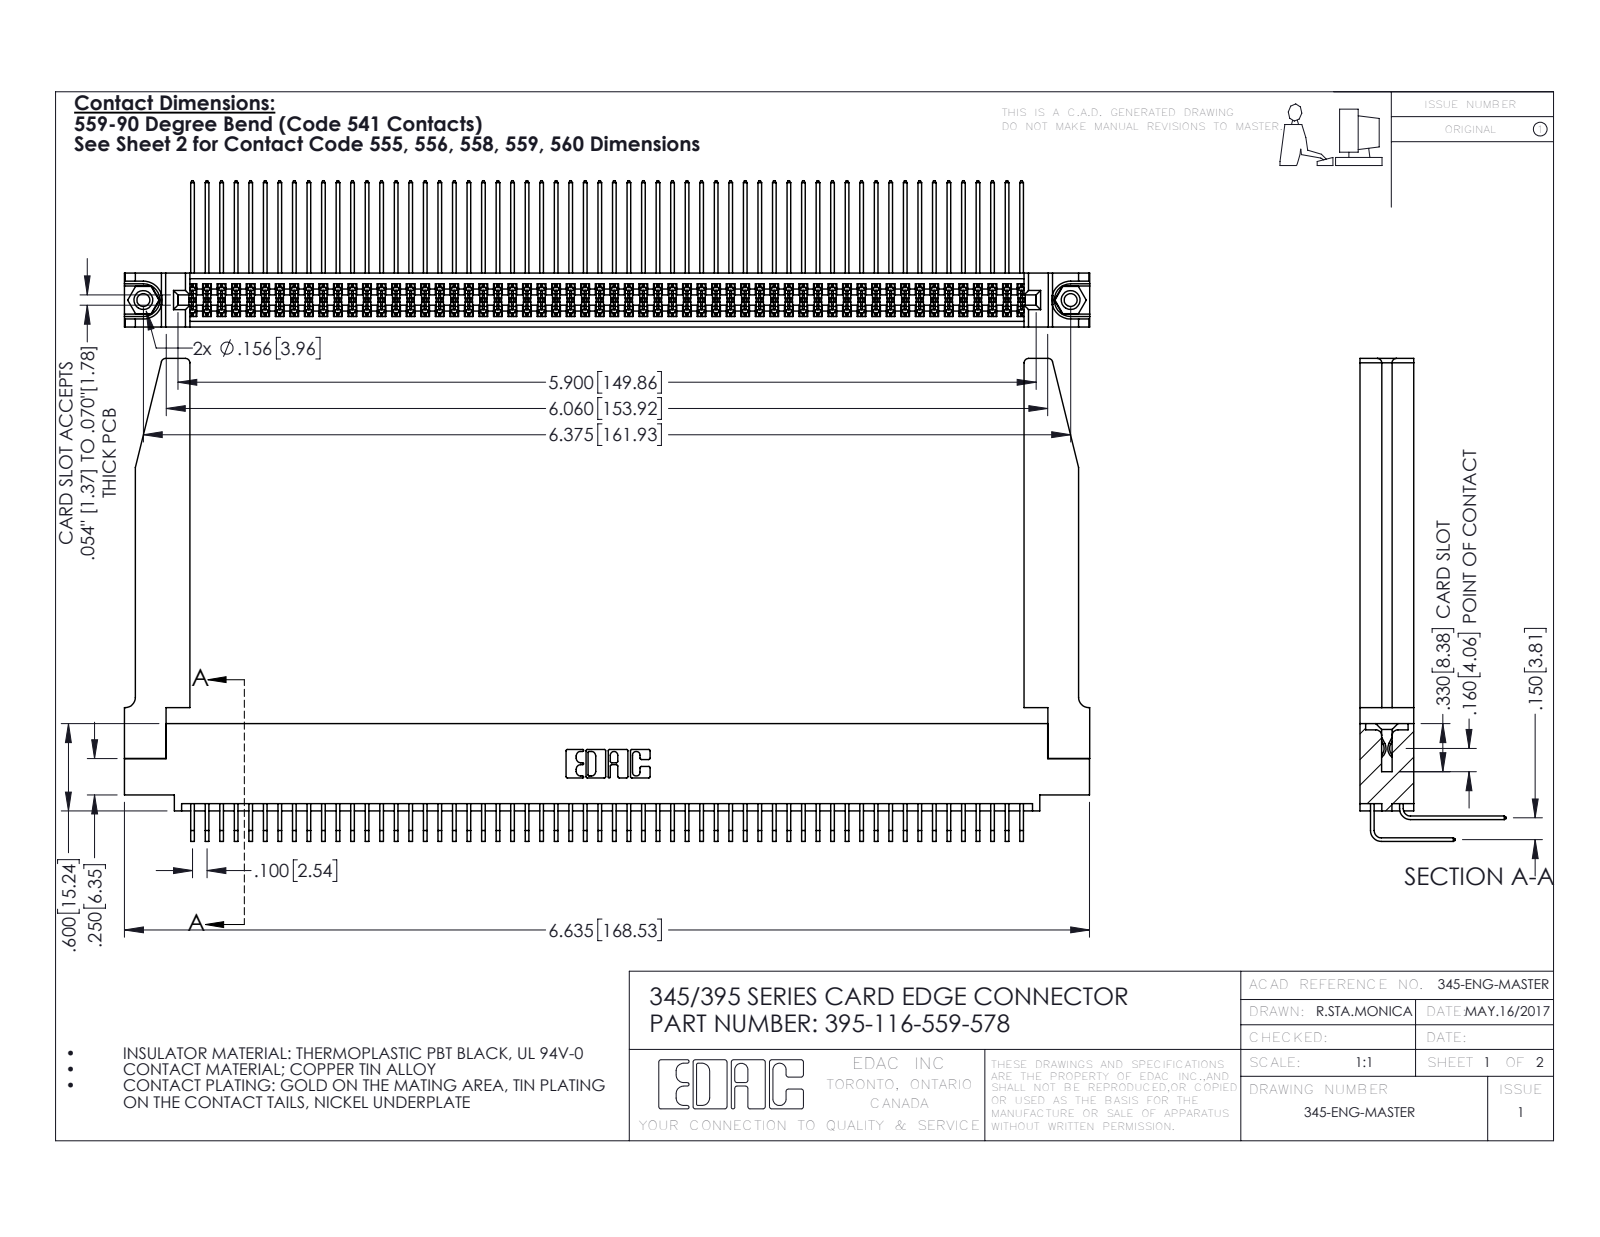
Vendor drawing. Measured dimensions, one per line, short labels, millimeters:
name: 345-292-001_558 559 Tail - 1; 345-220-078_345-220-078; 395-116-559-578; 345-292-001_559 Tail - 2 (+2 more)
written by: SolidWorks 2016 (CONFIG_CONTROL_DESIGN)
unit: mm
bodies: 121 solids, 6396 faces (4286 planar, 2058 cylindrical, 52 other)
size: 168.6 × 84.3 × 25.5
volume: 24 890 mm³; area: 35 690 mm²
holes: 2× ⌀2.3, 2× ⌀3.2, 2× ⌀4, 1× ⌀1.6
bosses: 2× ⌀3.9
rounds: 174× R0.2, 22× R0.3, 8× R0.8, 6× R0.2, 6× R0.8, 3× R0.7, 2× R0.4, 2× R0.5
face distances: 1.8, 7.6, 9.4, 5.1, 2.5, 6.9, 0.6, 5.7, 4.4, 3.8
hole spacings: 6.9, 155.9, 161.9
